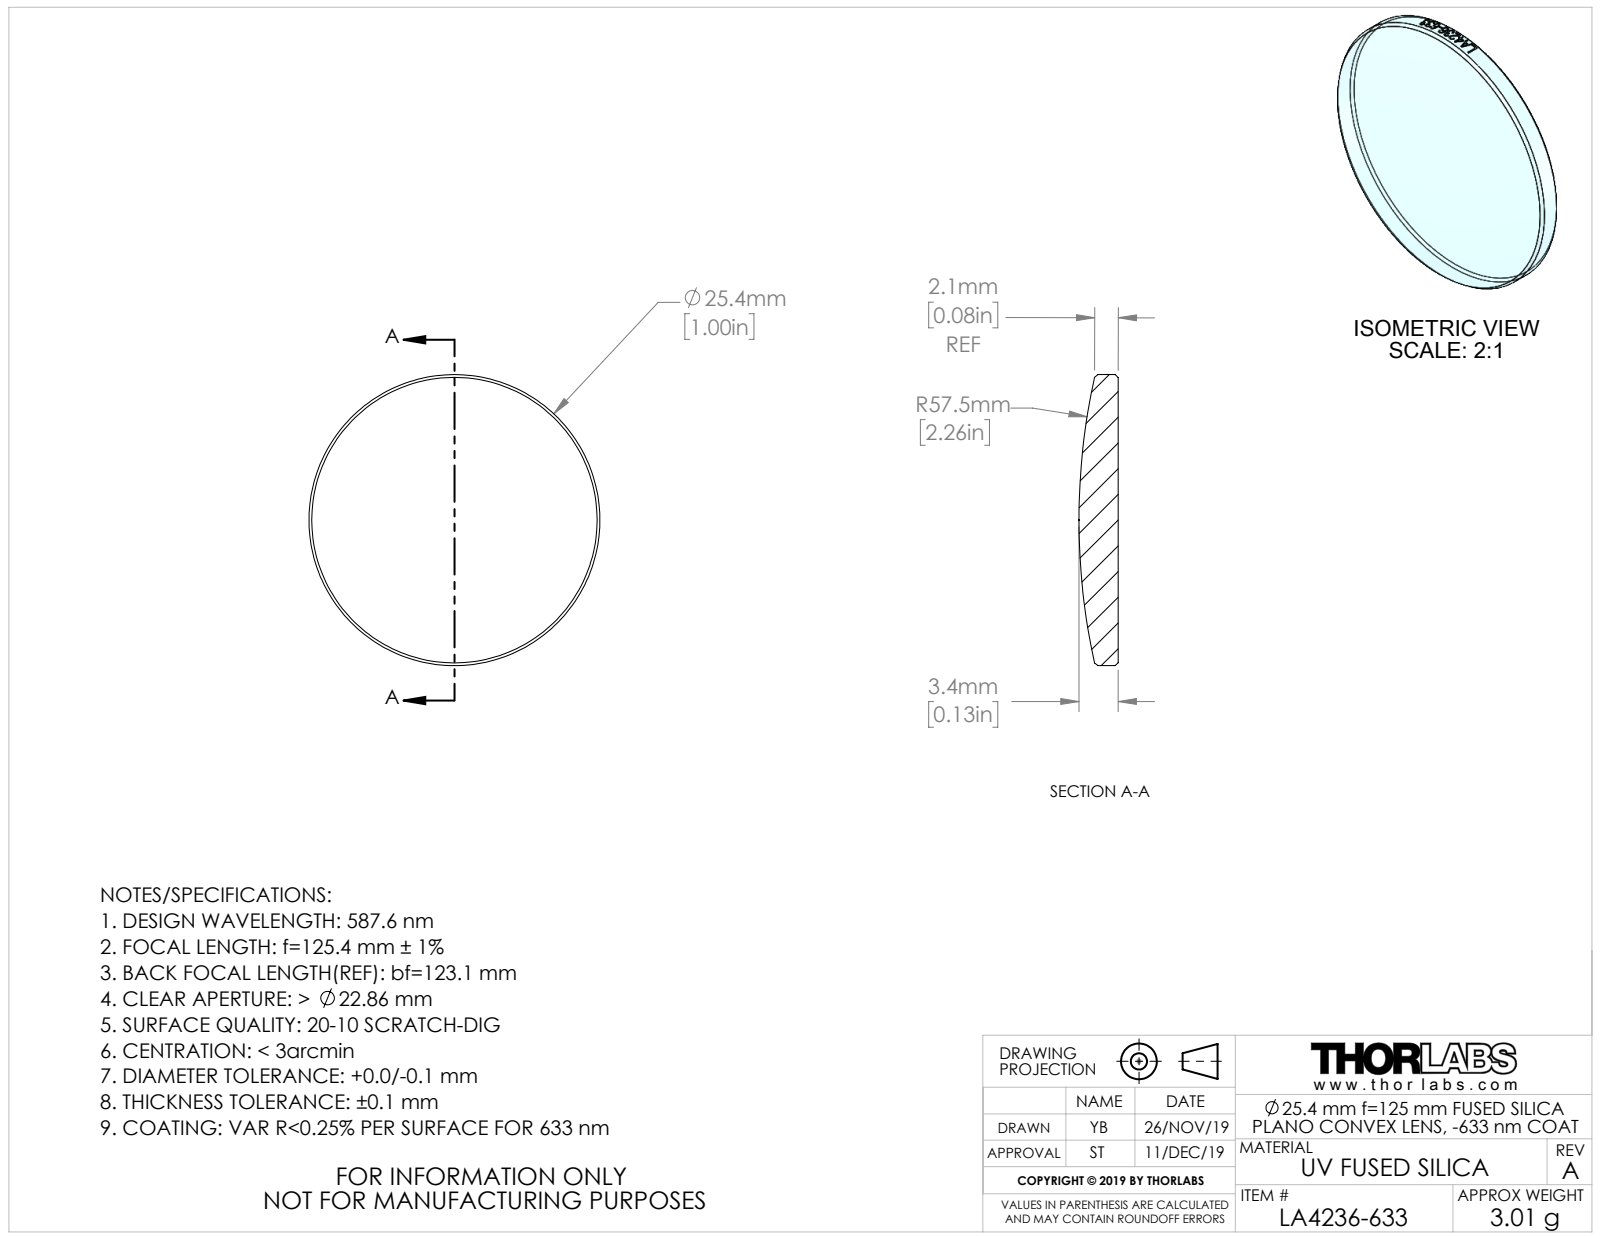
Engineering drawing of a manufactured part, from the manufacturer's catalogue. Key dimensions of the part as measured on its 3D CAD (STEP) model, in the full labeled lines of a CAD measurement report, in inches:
Part name (STEP PRODUCT): CTN015014; CTN014995-999
STEP written by: SolidWorks 2018 (AUTOMOTIVE_DESIGN)
Units: inches
Bodies: 1 solid, 29 faces (1 planar, 22 cylindrical, 6 other)
Overall size (bounding box): 1 × 1 × 0.134
Volume: 0.083 in³ · Surface area: 1.796 in²
Round bosses / shafts (diameter × count): ⌀1 ×1
